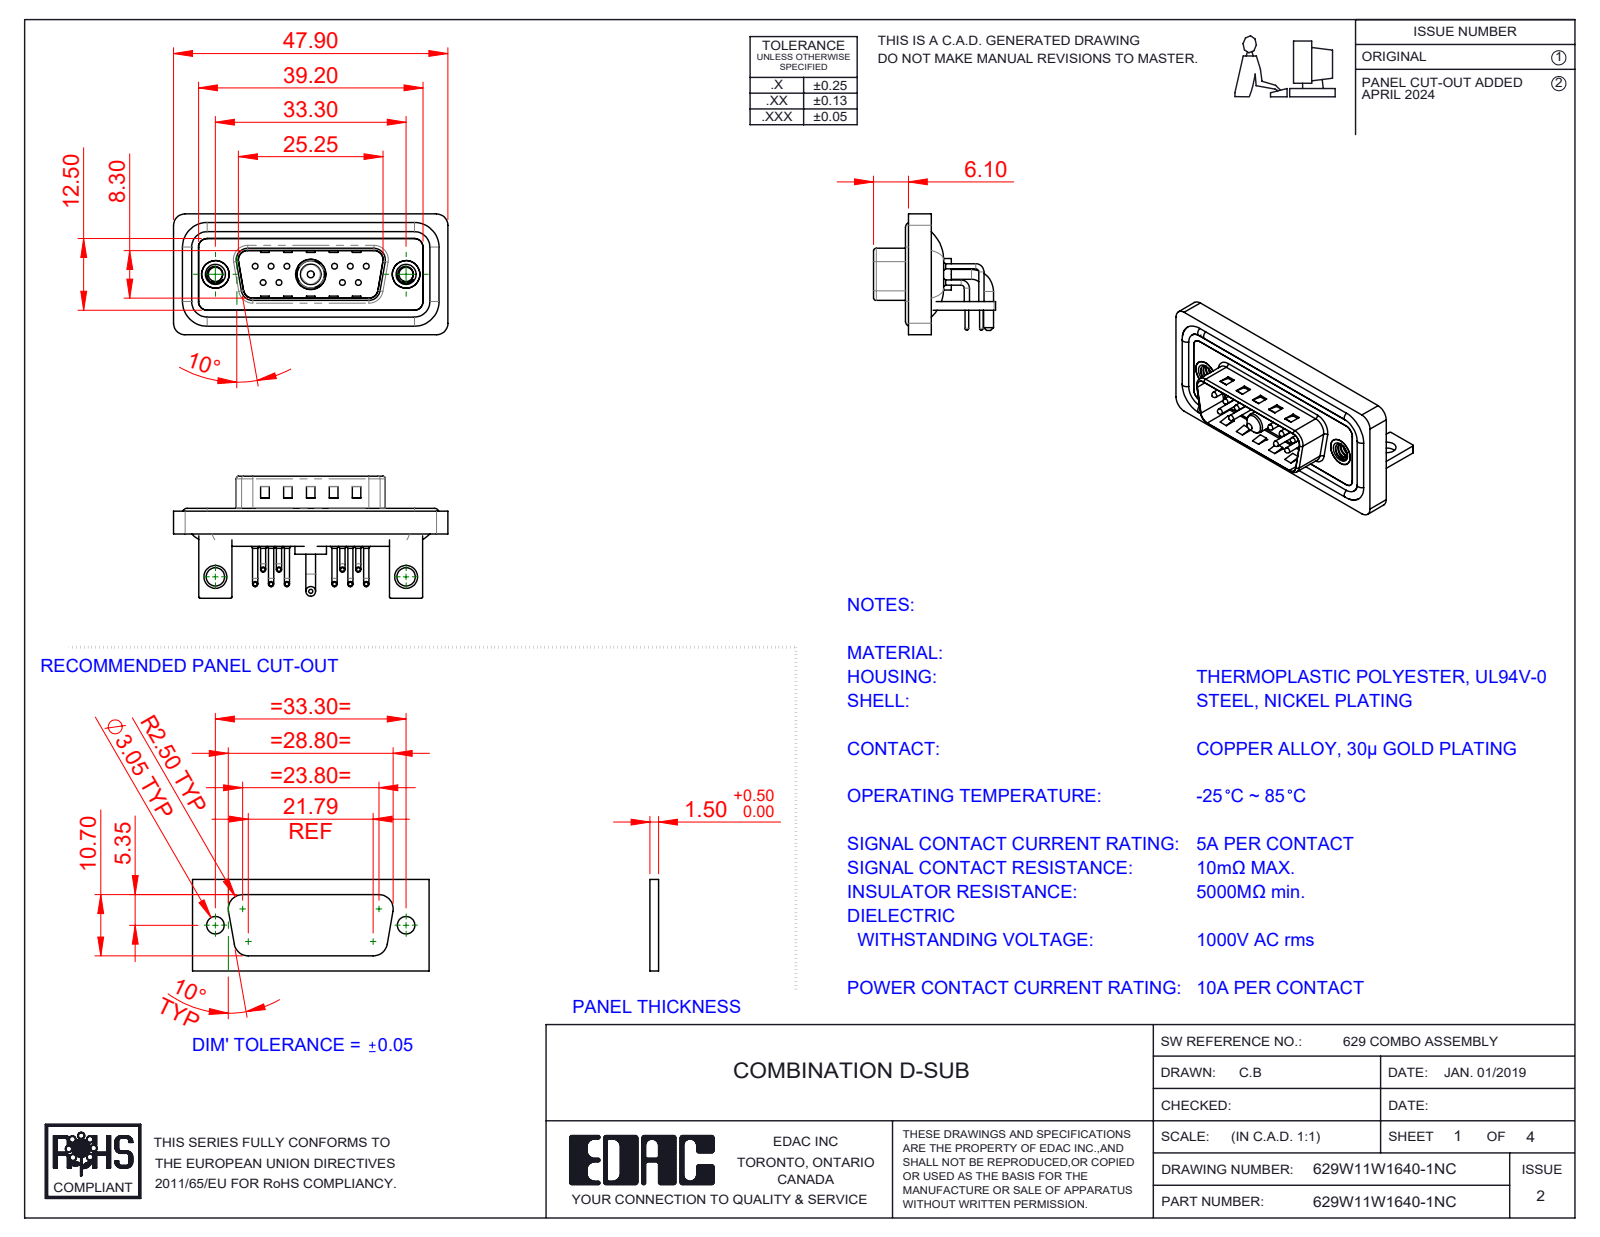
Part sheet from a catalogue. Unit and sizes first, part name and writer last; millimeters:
Units: millimetres
Overall size (bounding box): 47.9 × 21.3 × 21.1
Round holes (diameter × count): ⌀0.75 ×10, ⌀1.6 ×10, ⌀2 ×10, ⌀2.5 ×2, ⌀3.2 ×2, ⌀4 ×2, ⌀4.8 ×2, ⌀5 ×2, ⌀4.85 ×1, ⌀5.3 ×1
Round bosses / shafts (diameter × count): ⌀0.9 ×20, ⌀1.5 ×10, ⌀1 ×10, ⌀0.65 ×10, ⌀1.6 ×4, ⌀4.9 ×2, ⌀1.7 ×2, ⌀5.5 ×1
Partial cylindrical surfaces — rounded edges, fillets, slot ends (radius × count): R2 ×21, R1.5 ×18, R0.25 ×16, R1.01 ×10, R0.5 ×9, R1.6 ×8, R1 ×7, R0.6 ×4
Main face-to-face distances: 0.4, 0.8, 1.5, 2.9, 2.1, 1.1, 1.6, 1.2, 3.7, 4.1
Hole centre spacings: 3.16, 2.77, 13.85, 11.08, 16.62, 5.03, 5.04, 5.54
Volume: 5 803 mm³ · Surface area: 9 817 mm²
Bodies: 21 solids, 1641 faces (856 planar, 587 cylindrical, 198 other)
Part name (STEP PRODUCT): 629Combo Contact Row 2; 629W11W1640-1NC; 629Combo Contact Row 1; 629Combo Shell Front_15 Contacts (+6 more)
STEP written by: SolidWorks 2023 (CONFIG_CONTROL_DESIGN)
